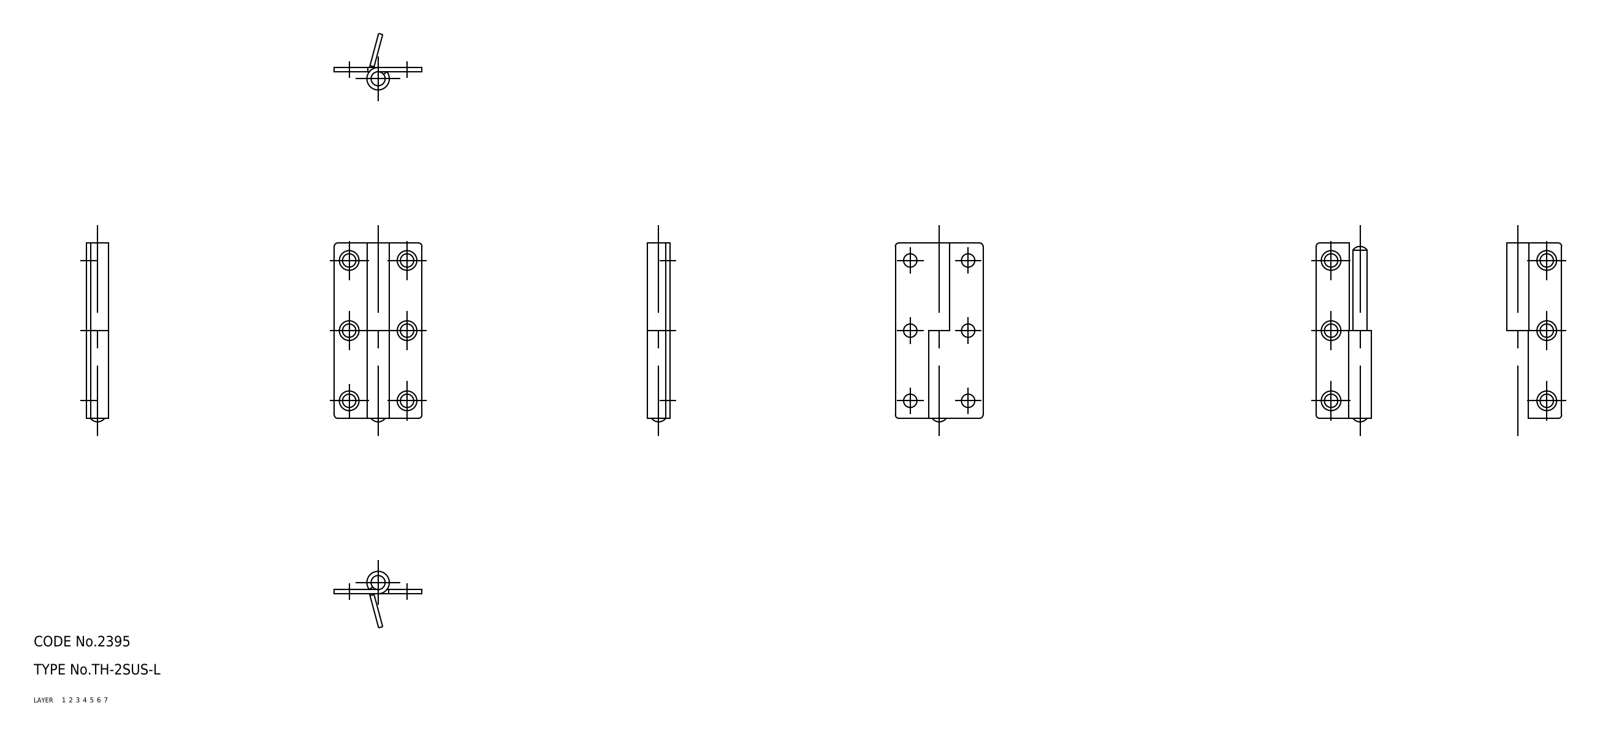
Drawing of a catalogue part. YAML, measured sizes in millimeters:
part_name: "shaft; hinge piece_B; hinge piece_A; TH_2SUS_L_7465_36"
step_written_by: "CADfix (AUTOMOTIVE_DESIGN)"
units: millimeters
bodies: {solids: 3, faces: 52, planar: 0, cylindrical: 0, other: 52}
overall_size: [51, 25, 6.4]
volume: 2659
surface_area: 4512
